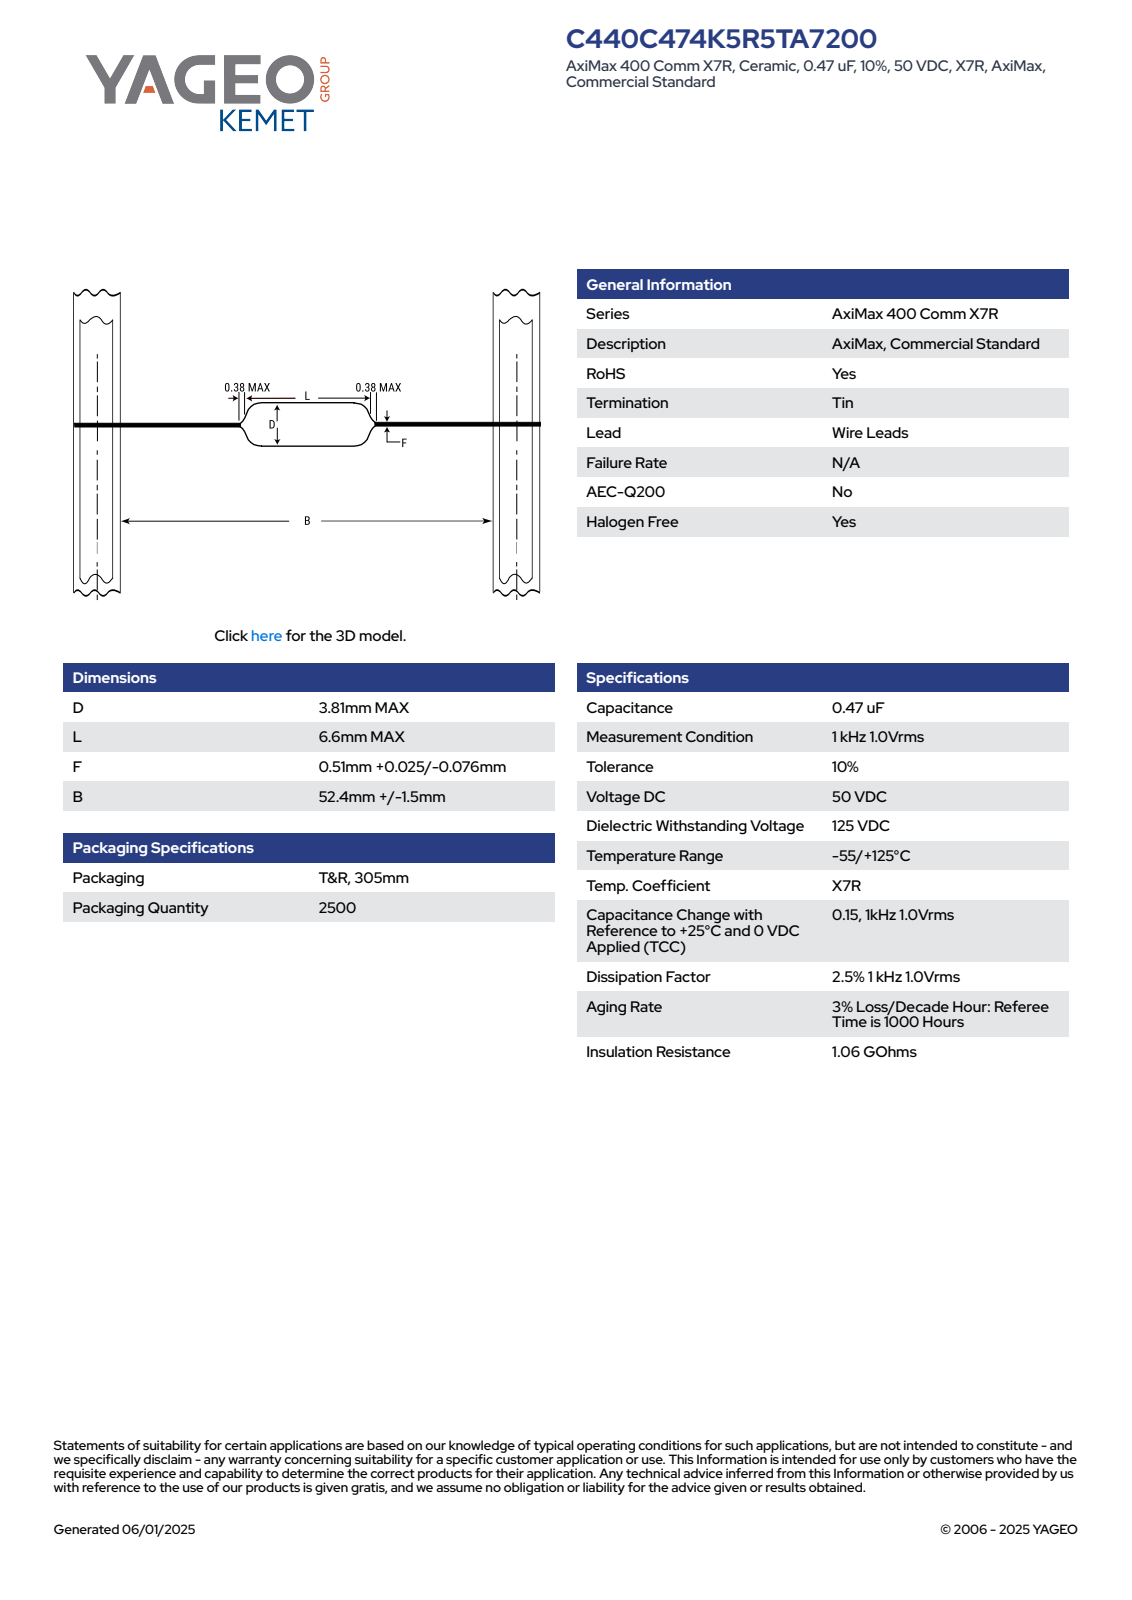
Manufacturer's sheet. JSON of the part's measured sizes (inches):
{"part_name": "CCA_ACSTTAPE_C440_D3.81L6.6LL25.4F0.535", "step_written_by": "SolidWorks 2014 (AUTOMOTIVE_DESIGN)", "units": "inches", "bodies": {"solids": 1, "faces": 74, "planar": 26, "cylindrical": 9, "other": 39}, "overall_size": [2.29, 0.15, 0.15], "volume_in3": 0.005, "surface_area_in2": 0.279, "round_bosses_or_shafts": [[0.15, 1], [0.021, 1]], "partial_cylinders_radius": [[0.075, 1]], "face_to_face_distances": [0.26, 1.015, 1.275, 2.29]}
